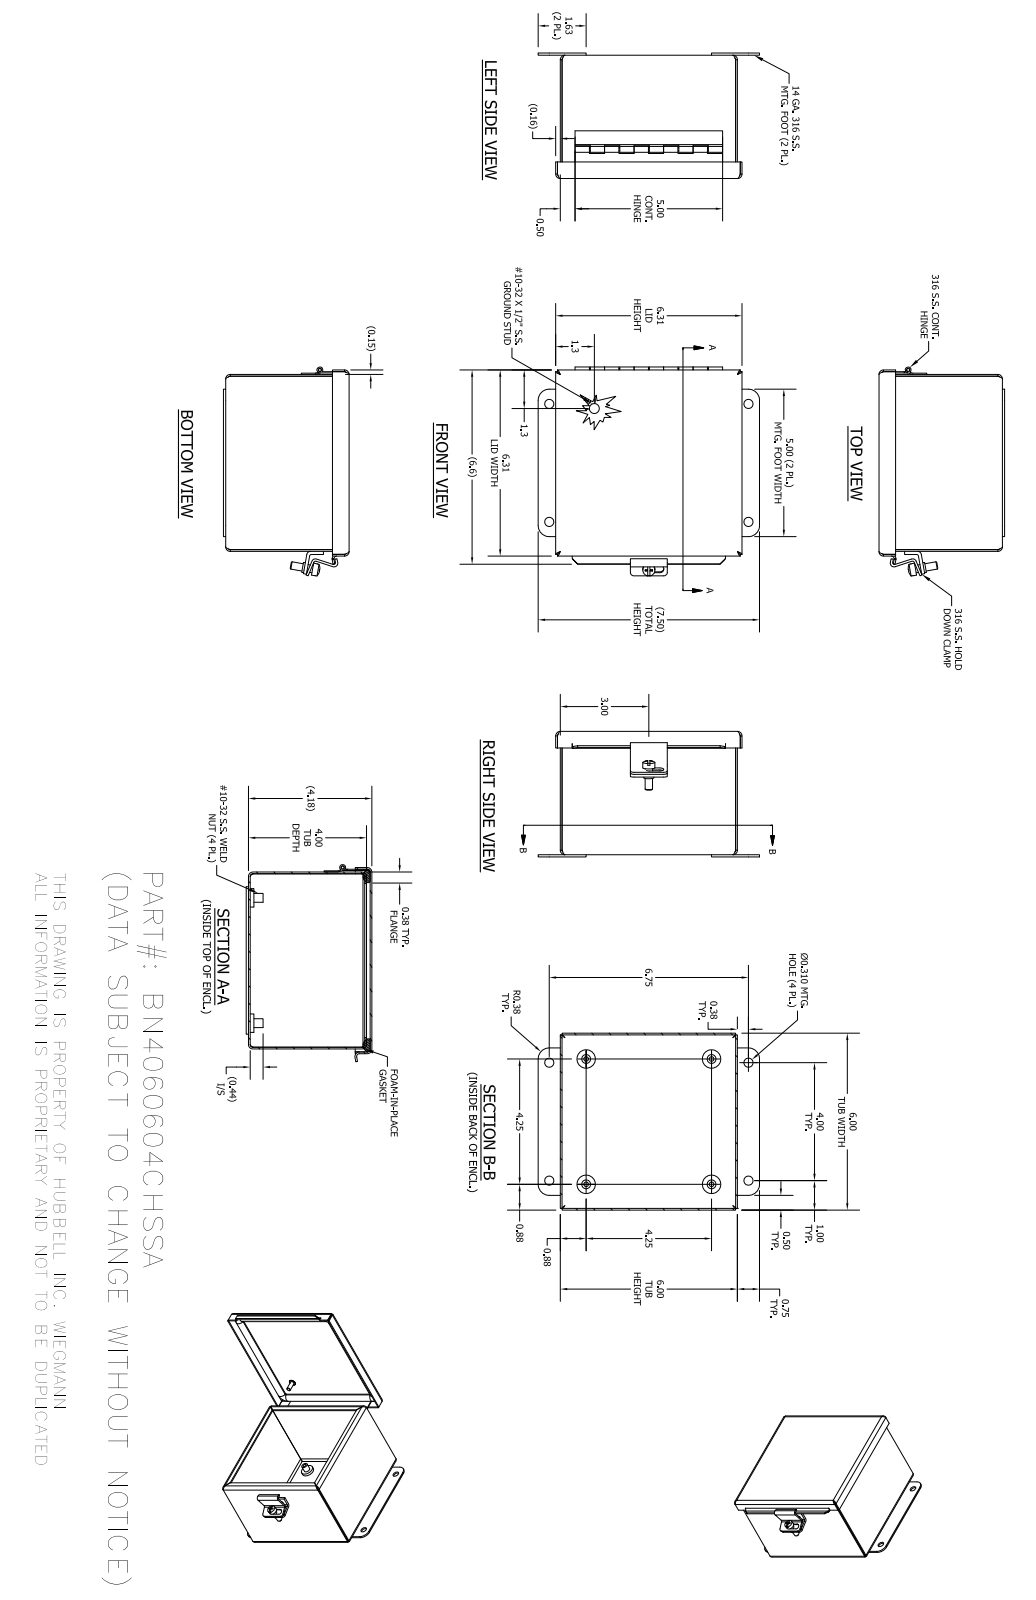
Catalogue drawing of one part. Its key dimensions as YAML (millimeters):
part_name: "B_060604_SSABKP; 32882LH; 32882P; 32882TH (+8 more)"
step_written_by: "Autodesk Inventor 2016 (AUTOMOTIVE_DESIGN)"
units: millimeters
bodies: {solids: 16, faces: 343, planar: 182, cylindrical: 101, other: 60}
overall_size: [190.5, 179.98, 108.11]
volume: 246076
surface_area: 303290
round_holes:
  - {diameter: 3.96, count: 4}
  - {diameter: 7.87, count: 4}
  - {diameter: 2.79, count: 2}
  - {diameter: 2.96, count: 1}
  - {diameter: 4.98, count: 1}
round_bosses_or_shafts:
  - {diameter: 15.88, count: 4}
  - {diameter: 7.62, count: 4}
  - {diameter: 10.4, count: 1}
  - {diameter: 8.74, count: 1}
  - {diameter: 8.56, count: 1}
  - {diameter: 6.35, count: 1}
  - {diameter: 5.08, count: 1}
  - {diameter: 4.83, count: 1}
partial_cylinders:
  - {radius: 2.38, count: 13}
  - {radius: 3.88, count: 13}
  - {radius: 1.68, count: 8}
  - {radius: 3.17, count: 4}
  - {radius: 5.78, count: 4}
  - {radius: 9.53, count: 4}
  - {radius: 1.6, count: 3}
  - {radius: 3.2, count: 3}
face_to_face_distances: [1.5, 150.9, 104.71, 152.4, 149.4, 106.21, 103.21, 1.9, 3.4, 106.61]
hole_center_spacings: [109.48, 31.91, 31.92, 101.6, 107.94, 107.95, 139.73, 139.74]
